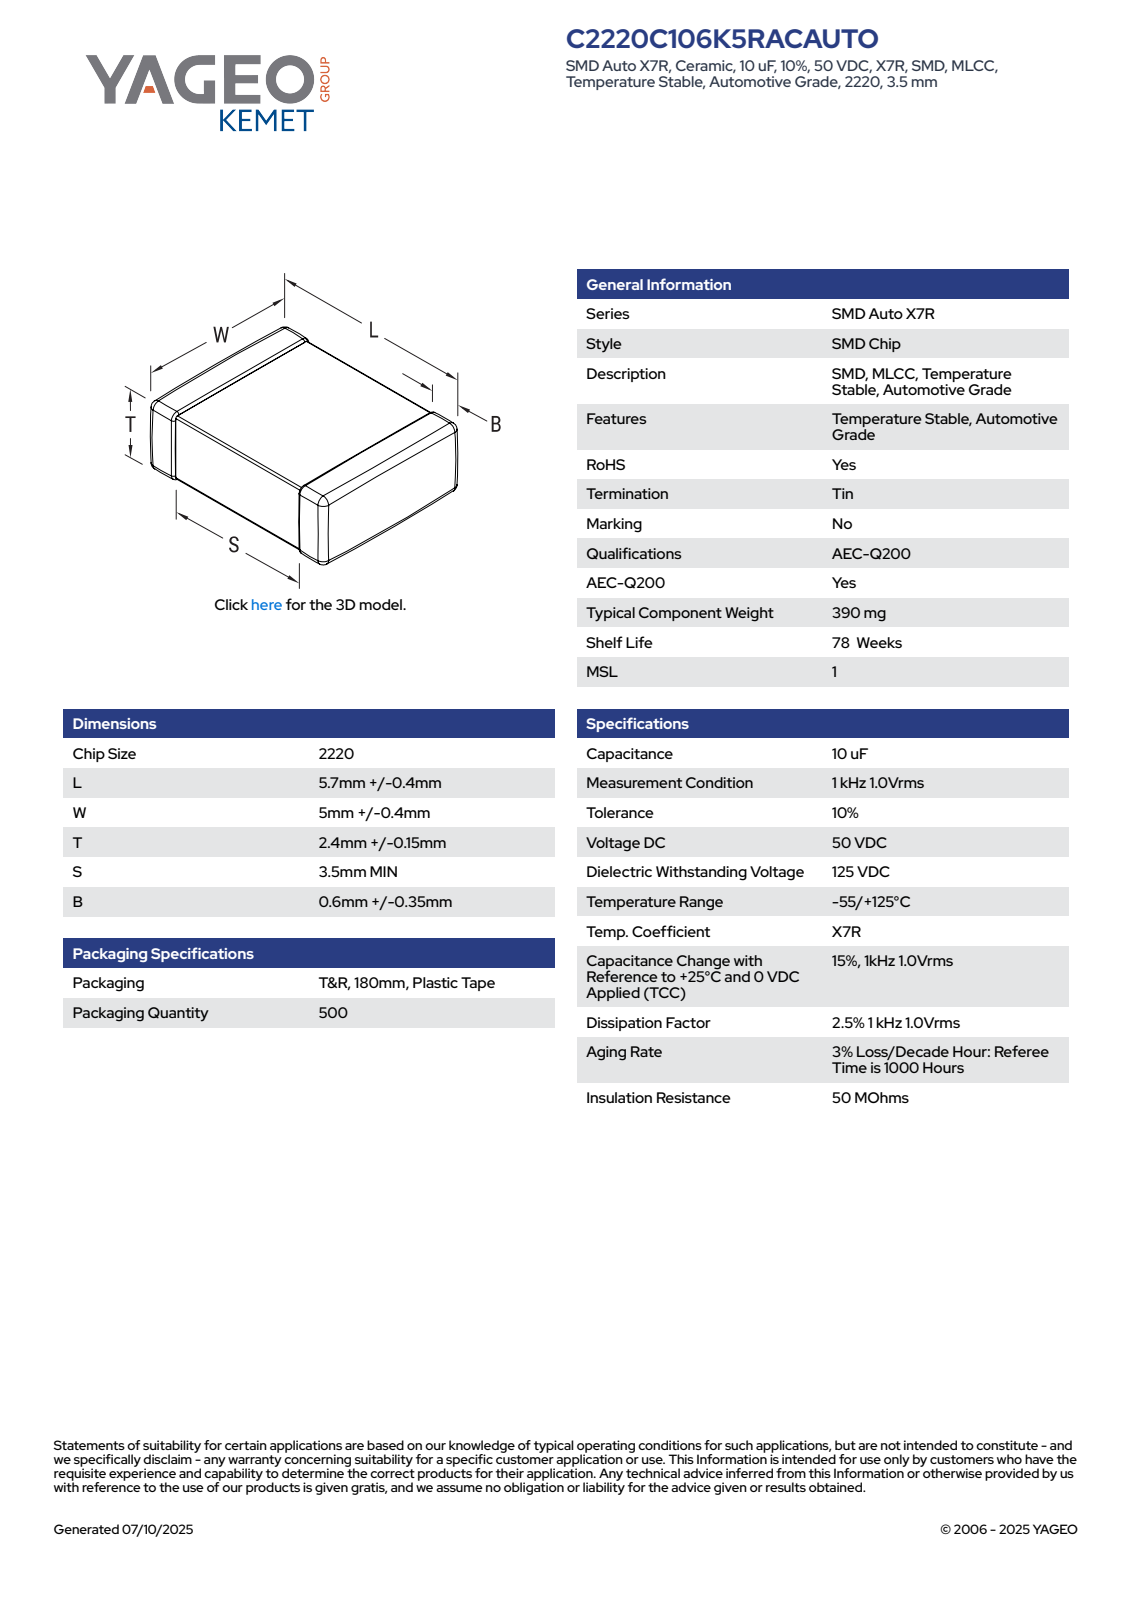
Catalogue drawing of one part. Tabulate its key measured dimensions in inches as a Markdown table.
| quantity | value |
| --- | --- |
| part name | CCS_CCSTD_2220_L6.1W5.4T2.55B0.6 |
| STEP written by | SolidWorks 2021 (AUTOMOTIVE_DESIGN) |
| units | inches |
| bodies | 4 solids, 125 faces (71 planar, 38 cylindrical, 16 other) |
| overall size | 0.24 × 0.213 × 0.1 |
| volume | 0.005 in³ |
| surface area | 0.192 in² |
| partial cylindrical surfaces (radius × count) | 0.004 × 24 |
| main face-to-face distances | 0.092, 0.096, 0.24, 0.204, 0.1, 0.208, 0.213, 0.098, 0.142, 0.13 |
